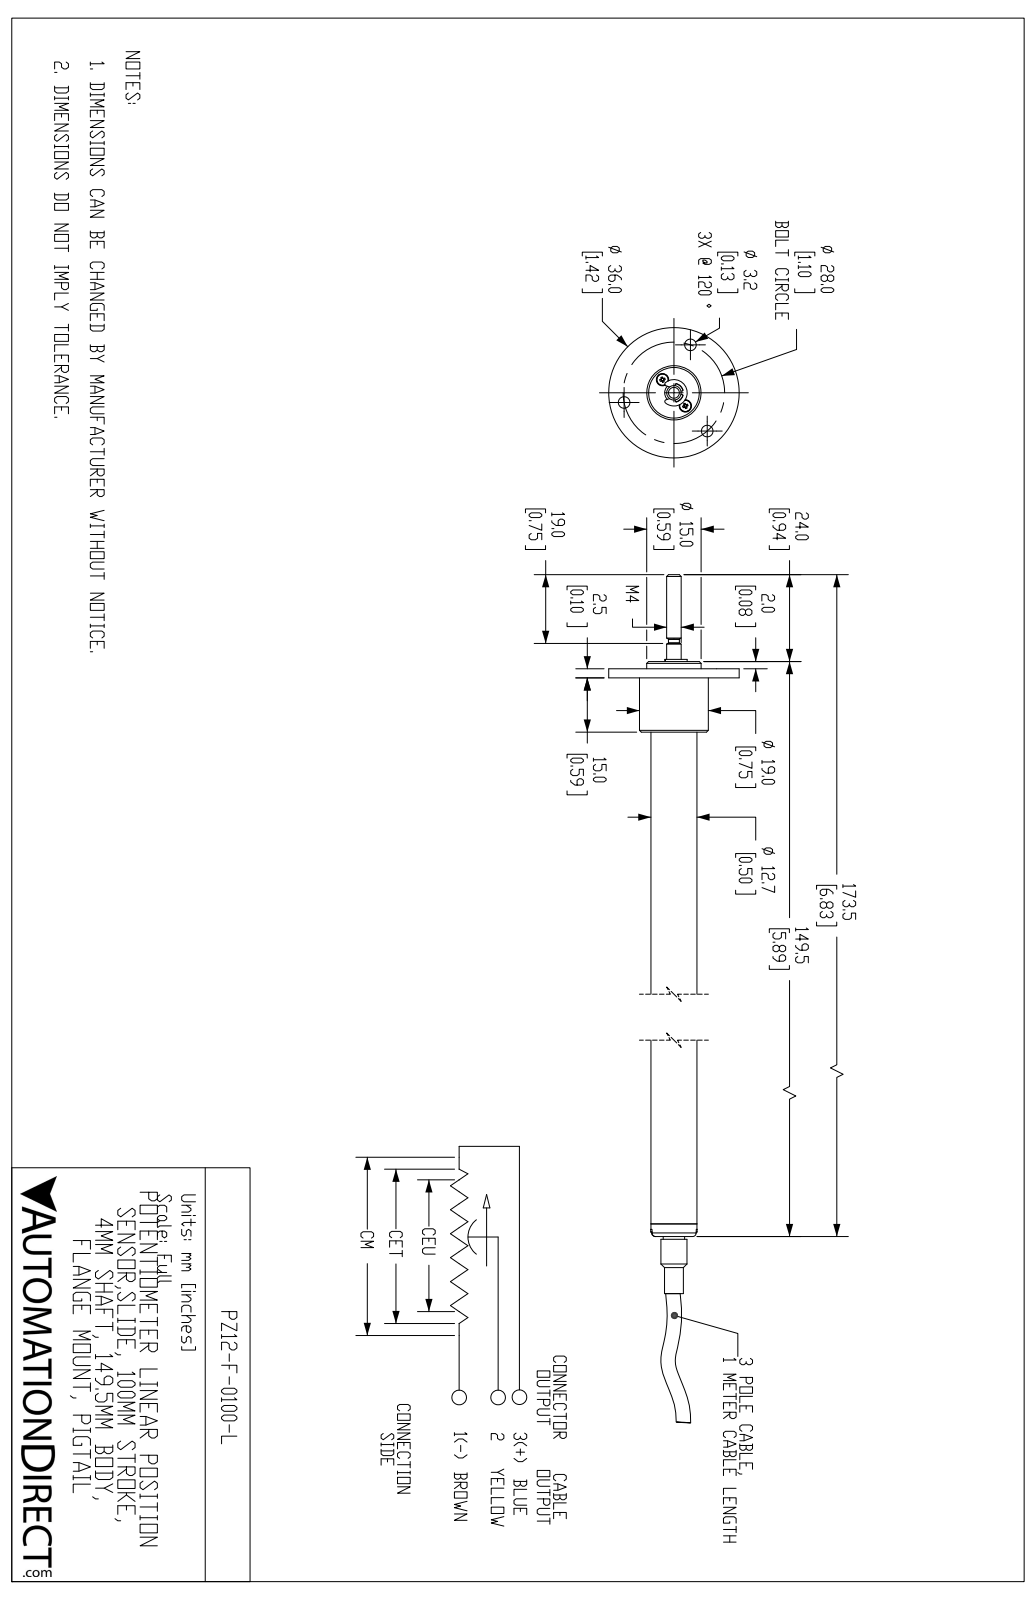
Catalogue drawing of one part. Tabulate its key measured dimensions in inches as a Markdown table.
| quantity | value |
| --- | --- |
| part name | PZ12-F-0100-L |
| STEP written by | SolidWorks 2019 (AUTOMOTIVE_DESIGN) |
| units | inches |
| bodies | 11 solids, 497 faces (129 planar, 135 cylindrical, 233 other) |
| overall size | 8.856 × 1.417 × 1.417 |
| volume | 1.553 in³ |
| surface area | 23.26 in² |
| round holes (diameter × count) | 0.126 × 4, 0.055 × 2, 0.079 × 2, 0.134 × 2, 0.039 × 1, 0.138 × 1, 0.201 × 1, 0.236 × 1, 0.502 × 1 |
| round bosses / shafts (diameter × count) | 0.126 × 4, 0.063 × 4, 1.417 × 1, 0.748 × 1, 0.591 × 1, 0.5 × 1, 0.283 × 1, 0.233 × 1 |
| partial cylindrical surfaces (radius × count) | 0.01 × 4, 0.02 × 2, 0.026 × 2, 0.069 × 2, 0.017 × 1, 0.103 × 1, 0.144 × 1 |
| main face-to-face distances | 0.098, 0.079, 0.177, 5.571, 5.669, 0.287, 5.748, 0.256, 5.492, 0.591 |
| hole center spacings | 0.189, 0.162, 0.341, 0.551, 0.666, 0.955, 0.363, 0.366 |
